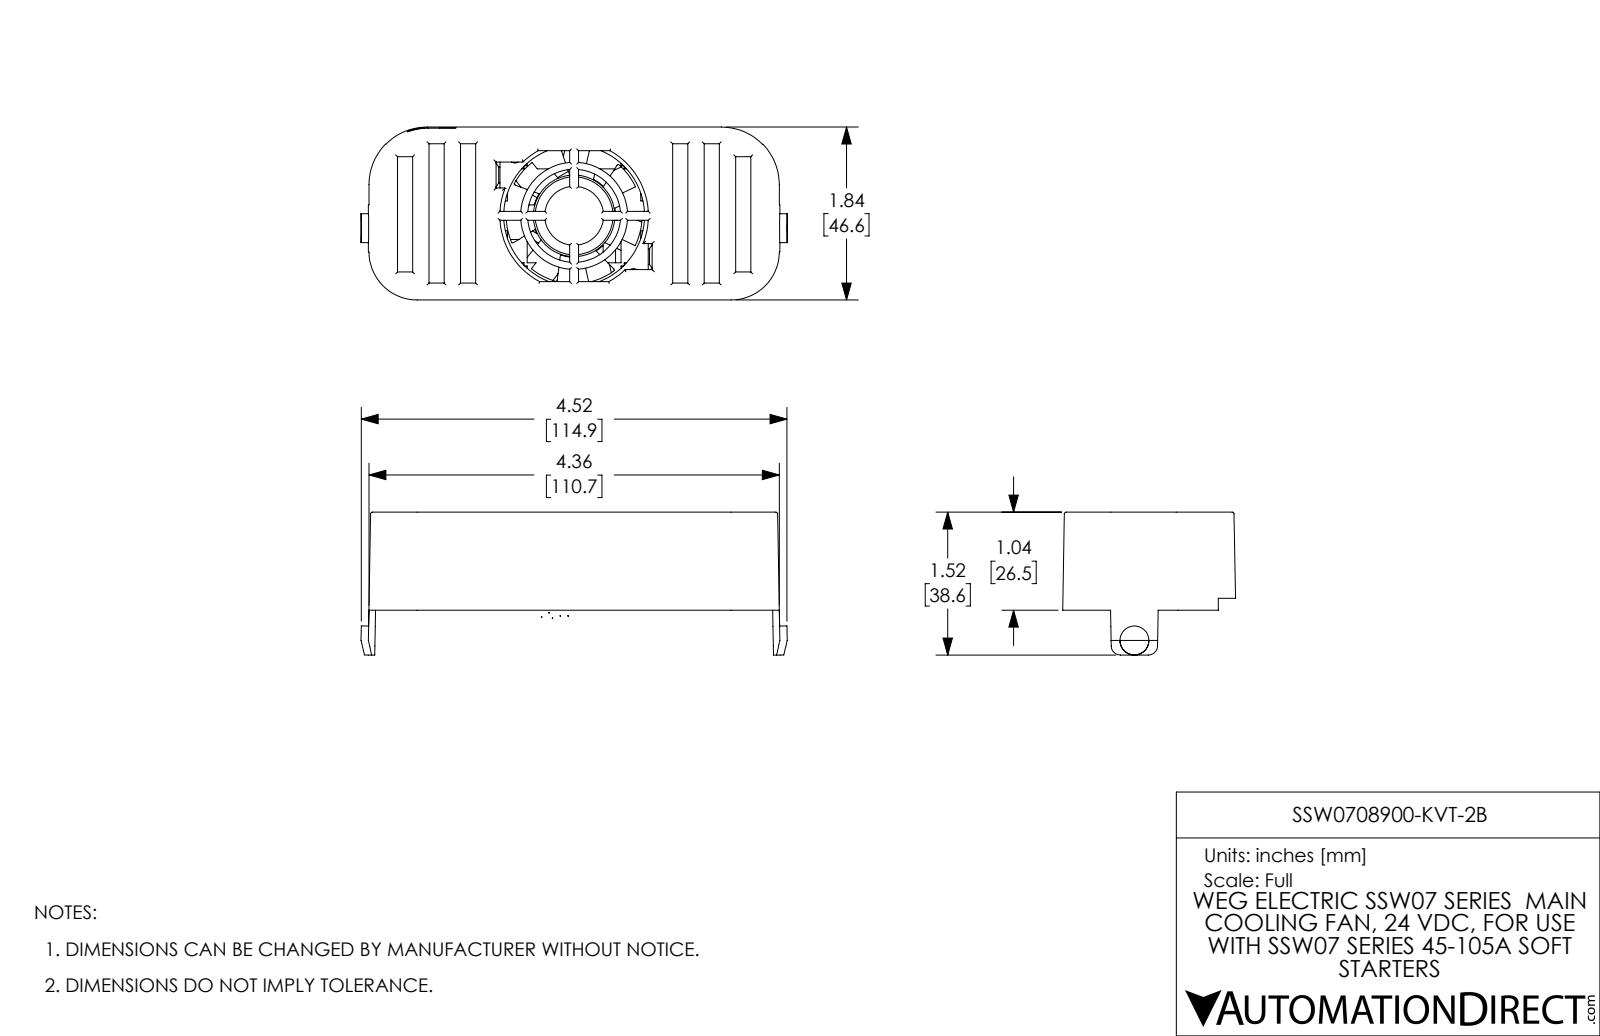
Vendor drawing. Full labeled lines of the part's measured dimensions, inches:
Part name (STEP PRODUCT): SSW0708900-KVT-2B b1
STEP written by: SolidWorks 2017 (AUTOMOTIVE_DESIGN)
Units: inches
Bodies: 9 solids, 570 faces (356 planar, 144 cylindrical, 70 other)
Overall size (bounding box): 4.529 × 1.836 × 1.518
Volume: 1.897 in³ · Surface area: 58.05 in²
Round holes (diameter × count): ⌀0.138 ×4, ⌀0.814 ×1, ⌀1.496 ×1
Round bosses / shafts (diameter × count): ⌀0.307 ×2, ⌀0.871 ×1, ⌀0.866 ×1
Partial cylindrical surfaces — rounded edges, fillets, slot ends (radius × count): R0.02 ×34, R0.079 ×4, R1.217 ×4, R0.098 ×2, R0.157 ×2, R0.551 ×2, R0.614 ×2, R0.44 ×1
Main face-to-face distances: 0.087, 0.07, 0.082, 0.791, 0.878, 0.302, 0.326, 0.628, 0.07, 0.759
Hole centre spacings: 0.891, 1.26, 1.781
